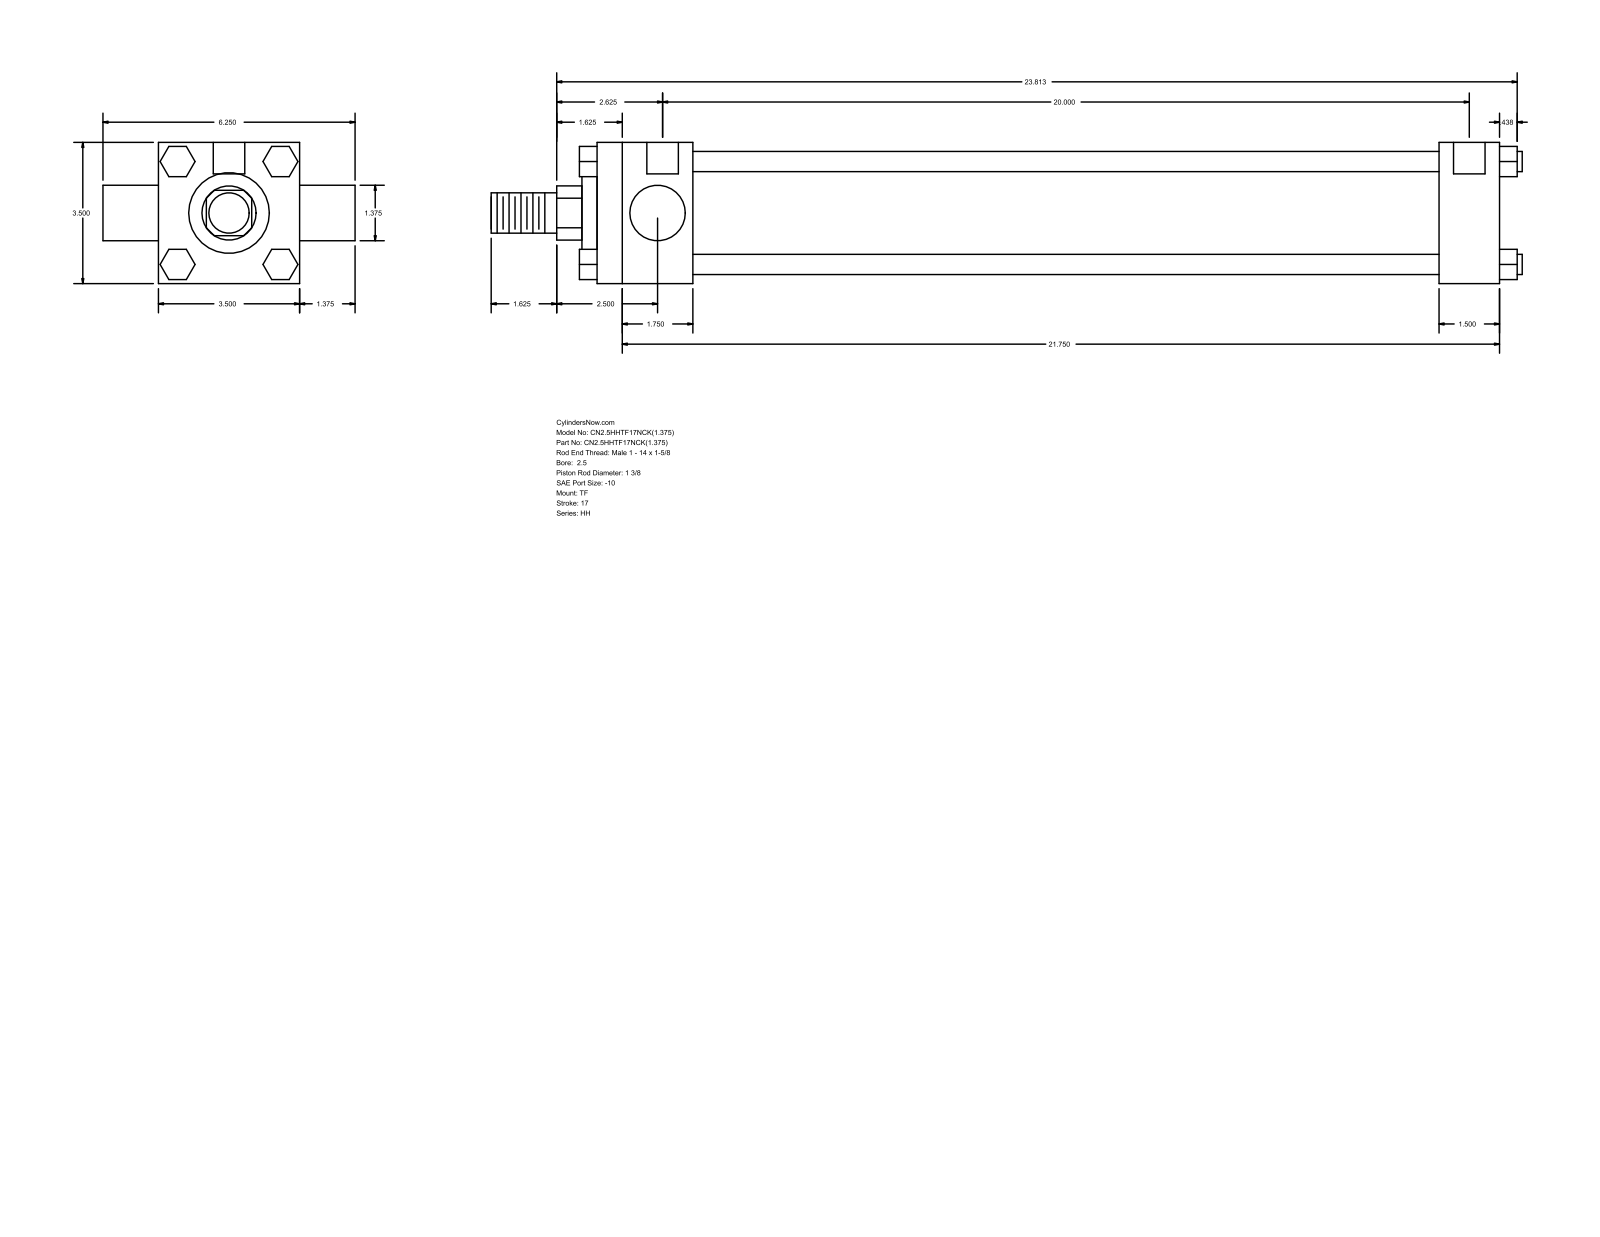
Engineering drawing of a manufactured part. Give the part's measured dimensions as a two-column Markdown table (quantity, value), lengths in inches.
| quantity | value |
| --- | --- |
| part name | HH_TF__0250_1.375 |
| STEP written by | GSSL Pune (CONFIG_CONTROL_DESIGN) |
| units | inches |
| bodies | 0 solids, 120 faces (92 planar, 28 cylindrical, 0 other) |
| overall size | 25.563 × 6.25 × 3.5 |
| round holes (diameter × count) | 0.219 × 3, 0.781 × 2 |
| round bosses / shafts (diameter × count) | 0.5 × 4, 1.375 × 2, 2.875 × 1, 2 × 1, 1 × 1 |
| partial cylindrical surfaces (radius × count) | 0.672 × 1 |
| main face-to-face distances | 3.5, 22.375, 2.375, 20, 20.875, 18.5, 1.5, 0.75, 1.275, 2.208 |
| hole center spacings | 0.062, 0.063, 20, 20.062, 20.063, 20.125 |
